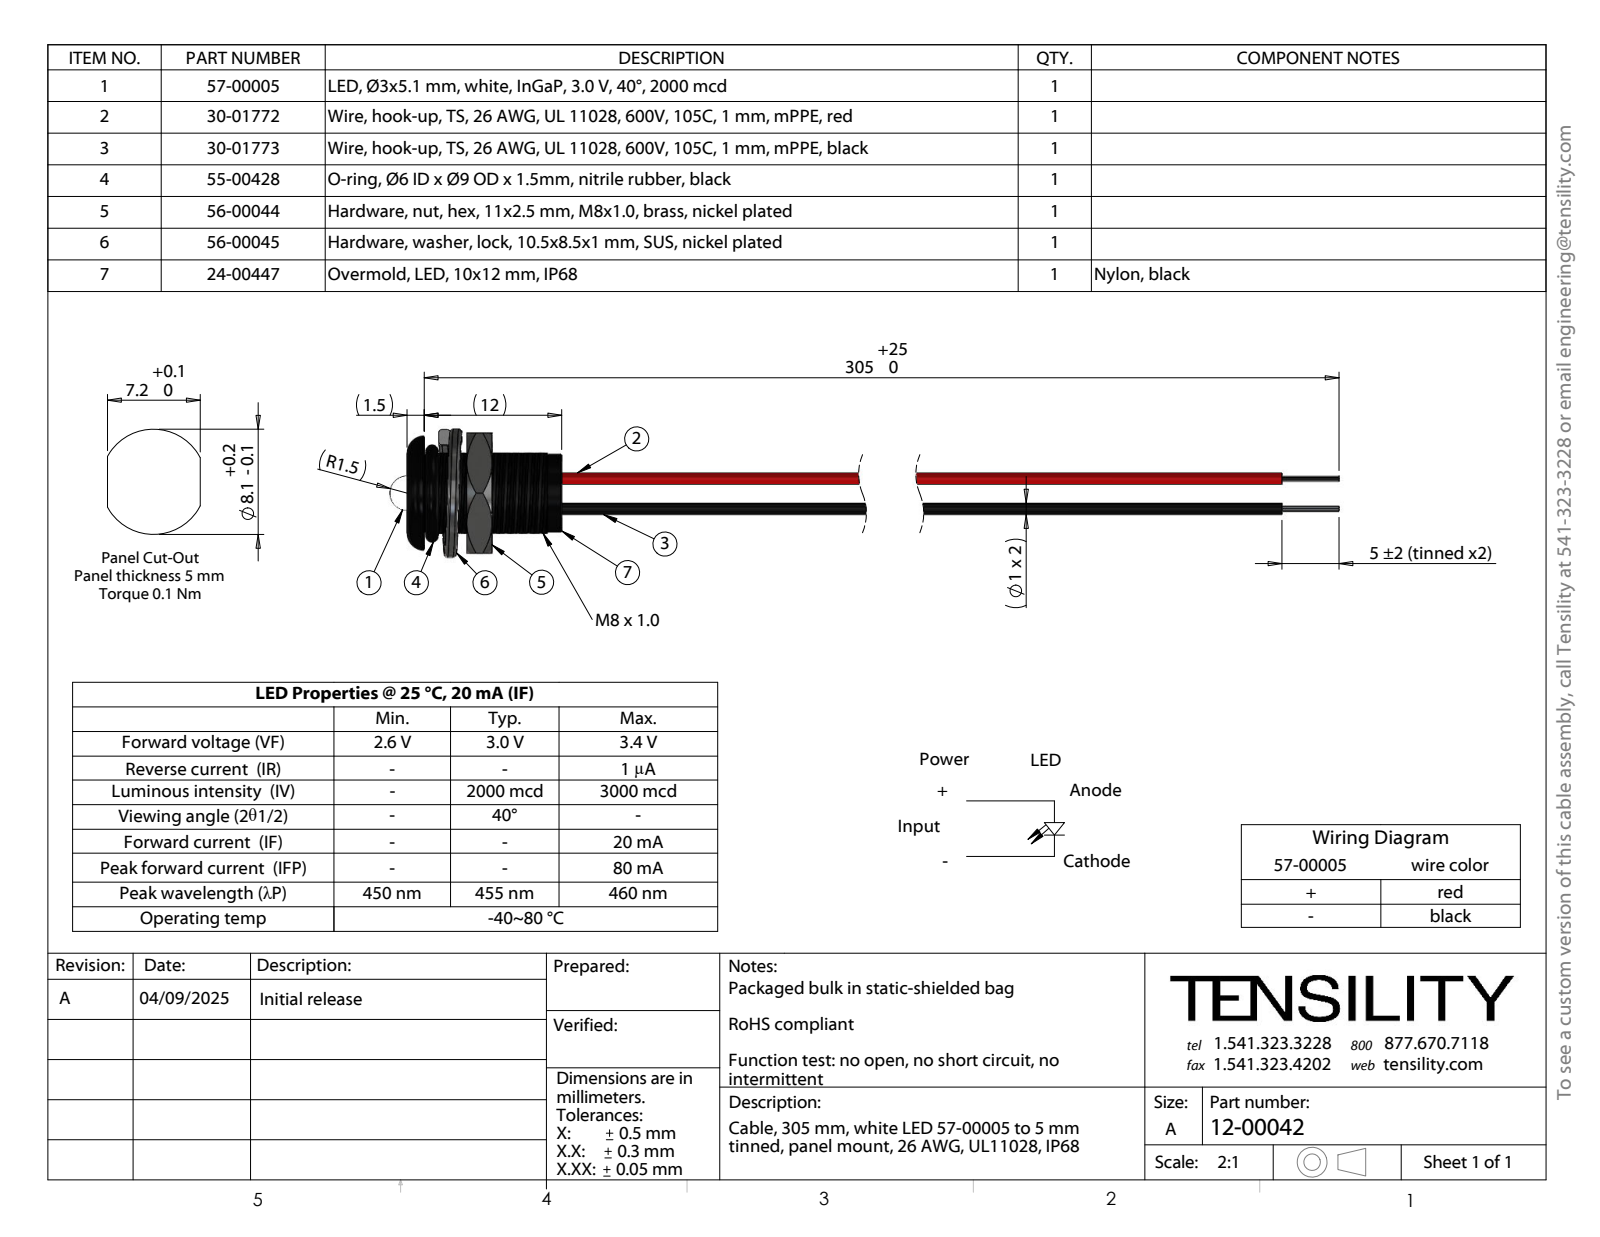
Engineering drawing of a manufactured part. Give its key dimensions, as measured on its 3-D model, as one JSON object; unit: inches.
{"part_name": "56-00045_Split washer; 30-01772_stripped and tinned; 12-00042; 56-00044 (+4 more)", "step_written_by": "SolidWorks 2021 (CONFIG_CONTROL_DESIGN)", "units": "inches", "bodies": {"solids": 57, "faces": 555, "planar": 186, "cylindrical": 246, "other": 123}, "overall_size": [6.693, 0.477, 0.441], "volume_in3": 0.061, "surface_area_in2": 9.157, "round_holes": [[0.039, 2]], "round_bosses_or_shafts": [[0.039, 2], [0.02, 2], [0.268, 1], [0.118, 1]], "partial_cylinders_radius": [[0.137, 1], [0.157, 1]], "face_to_face_distances": [0.059, 0.531, 0.472, 0.413, 0.205, 0.146, 0.326, 0.292, 0.233, 0.087], "hole_center_spacings": [0.014, 0.015, 0.013, 0.098, 0.099, 0.096, 0.096, 0.101]}
